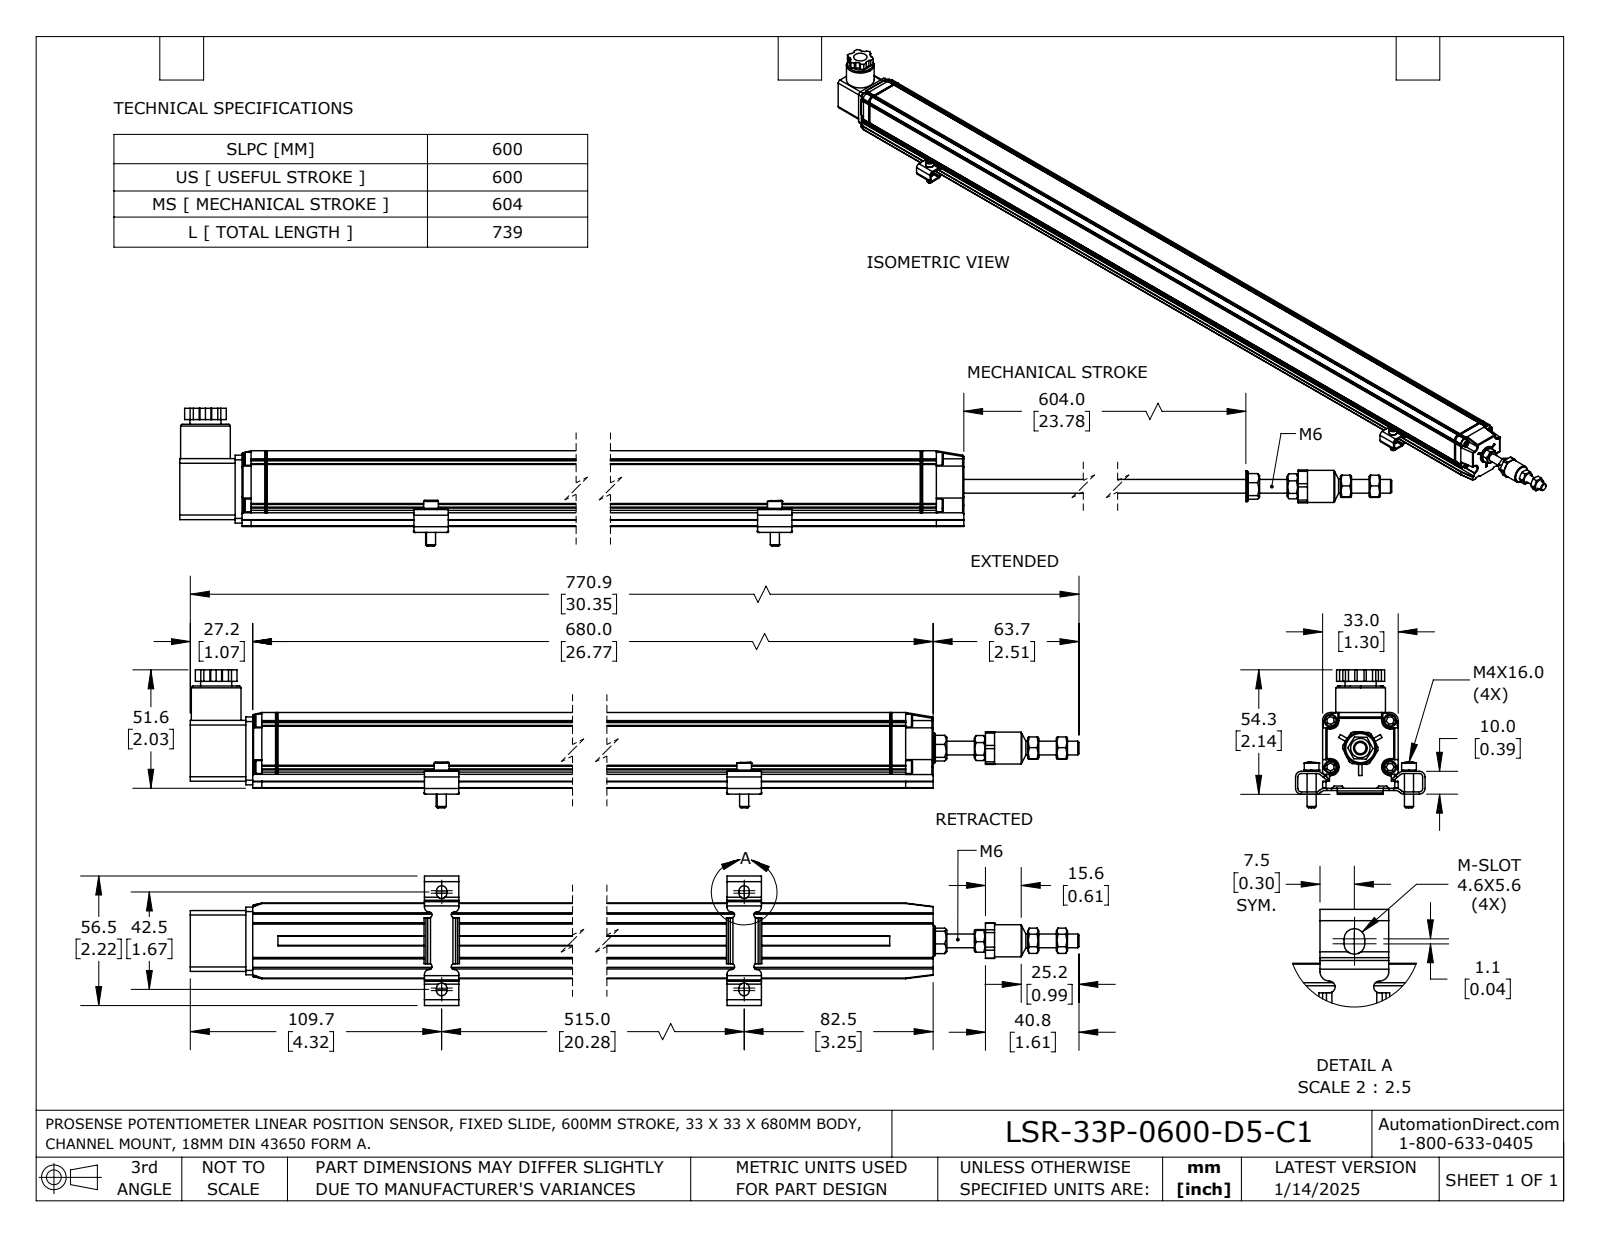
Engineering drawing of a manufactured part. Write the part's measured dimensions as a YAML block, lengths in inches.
part_name: "LSR-33P-0600-D5-C1"
step_written_by: "SolidWorks 2023 (AUTOMOTIVE_DESIGN)"
units: inches
bodies: {solids: 14, faces: 995, planar: 641, cylindrical: 269, other: 85}
overall_size: [30.348, 2.37, 2.224]
volume: 41.82
surface_area: 257.1
round_holes:
  - {diameter: 0.106, count: 4}
  - {diameter: 0.13, count: 4}
  - {diameter: 0.169, count: 1}
  - {diameter: 0.205, count: 1}
  - {diameter: 0.209, count: 1}
  - {diameter: 0.232, count: 1}
  - {diameter: 0.276, count: 1}
  - {diameter: 0.285, count: 1}
  - {diameter: 0.394, count: 1}
  - {diameter: 0.413, count: 1}
  - {diameter: 0.573, count: 1}
  - {diameter: 0.602, count: 1}
round_bosses_or_shafts:
  - {diameter: 0.157, count: 5}
  - {diameter: 0.118, count: 5}
  - {diameter: 0.256, count: 4}
  - {diameter: 0.22, count: 4}
  - {diameter: 0.854, count: 1}
  - {diameter: 0.551, count: 1}
  - {diameter: 0.535, count: 1}
  - {diameter: 0.528, count: 1}
partial_cylinders:
  - {radius: 0.079, count: 28}
  - {radius: 0.02, count: 23}
  - {radius: 0.008, count: 16}
  - {radius: 0.051, count: 8}
  - {radius: 0.059, count: 8}
  - {radius: 0.089, count: 8}
  - {radius: 0.118, count: 8}
  - {radius: 0.039, count: 4}
face_to_face_distances: [1.299, 0.118, 0.22, 1.181, 1.079, 0.039, 0.079, 0.142, 1.22, 0.185]
hole_center_spacings: [0.047, 0.583, 0.607, 0.696, 0.73, 0.799, 1.024, 1.299]
